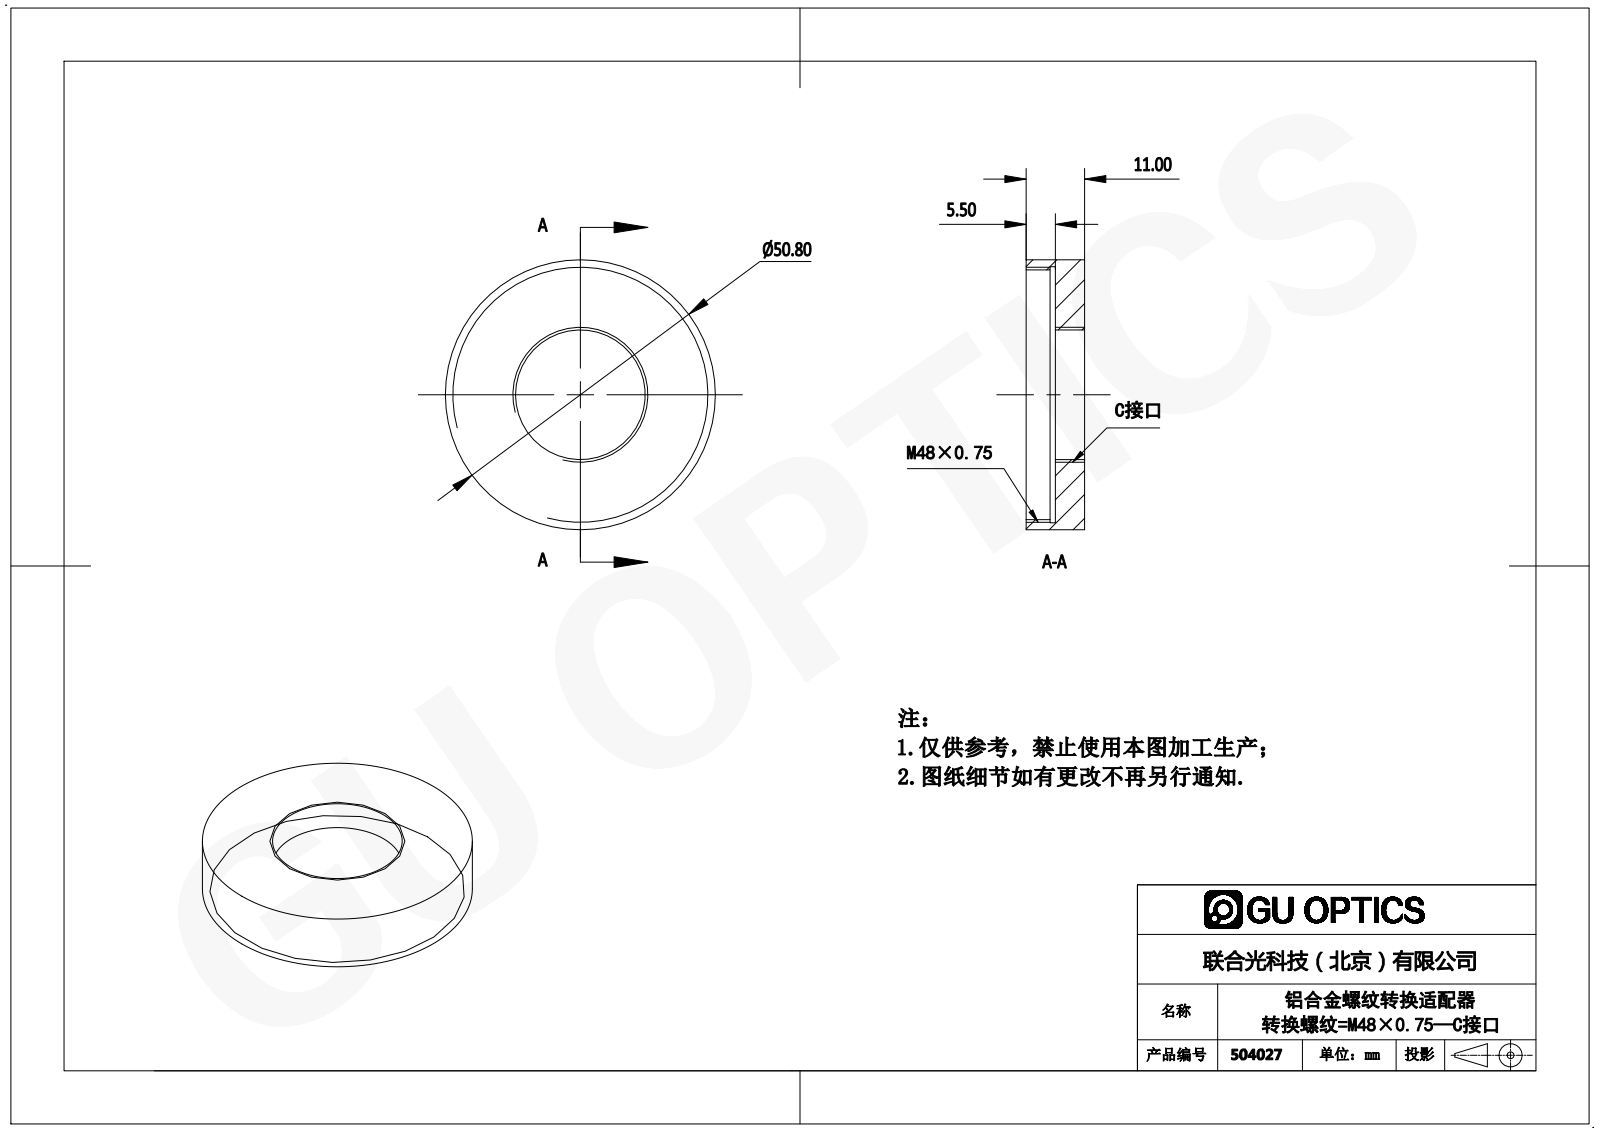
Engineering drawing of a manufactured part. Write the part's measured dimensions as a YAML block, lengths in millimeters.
part_name: "504027"
step_written_by: "SolidWorks 2016 (AUTOMOTIVE_DESIGN)"
units: millimeters
bodies: {solids: 1, faces: 12, planar: 4, cylindrical: 8, other: 0}
overall_size: [50.8, 50.8, 11]
volume: 10091
surface_area: 6291
round_holes:
  - {diameter: 24.4, count: 1}
  - {diameter: 47, count: 1}
  - {diameter: 48.2, count: 1}
round_bosses_or_shafts:
  - {diameter: 50.8, count: 1}
face_to_face_distances: [5.5, 11, 4.5, 1, 6.5]
